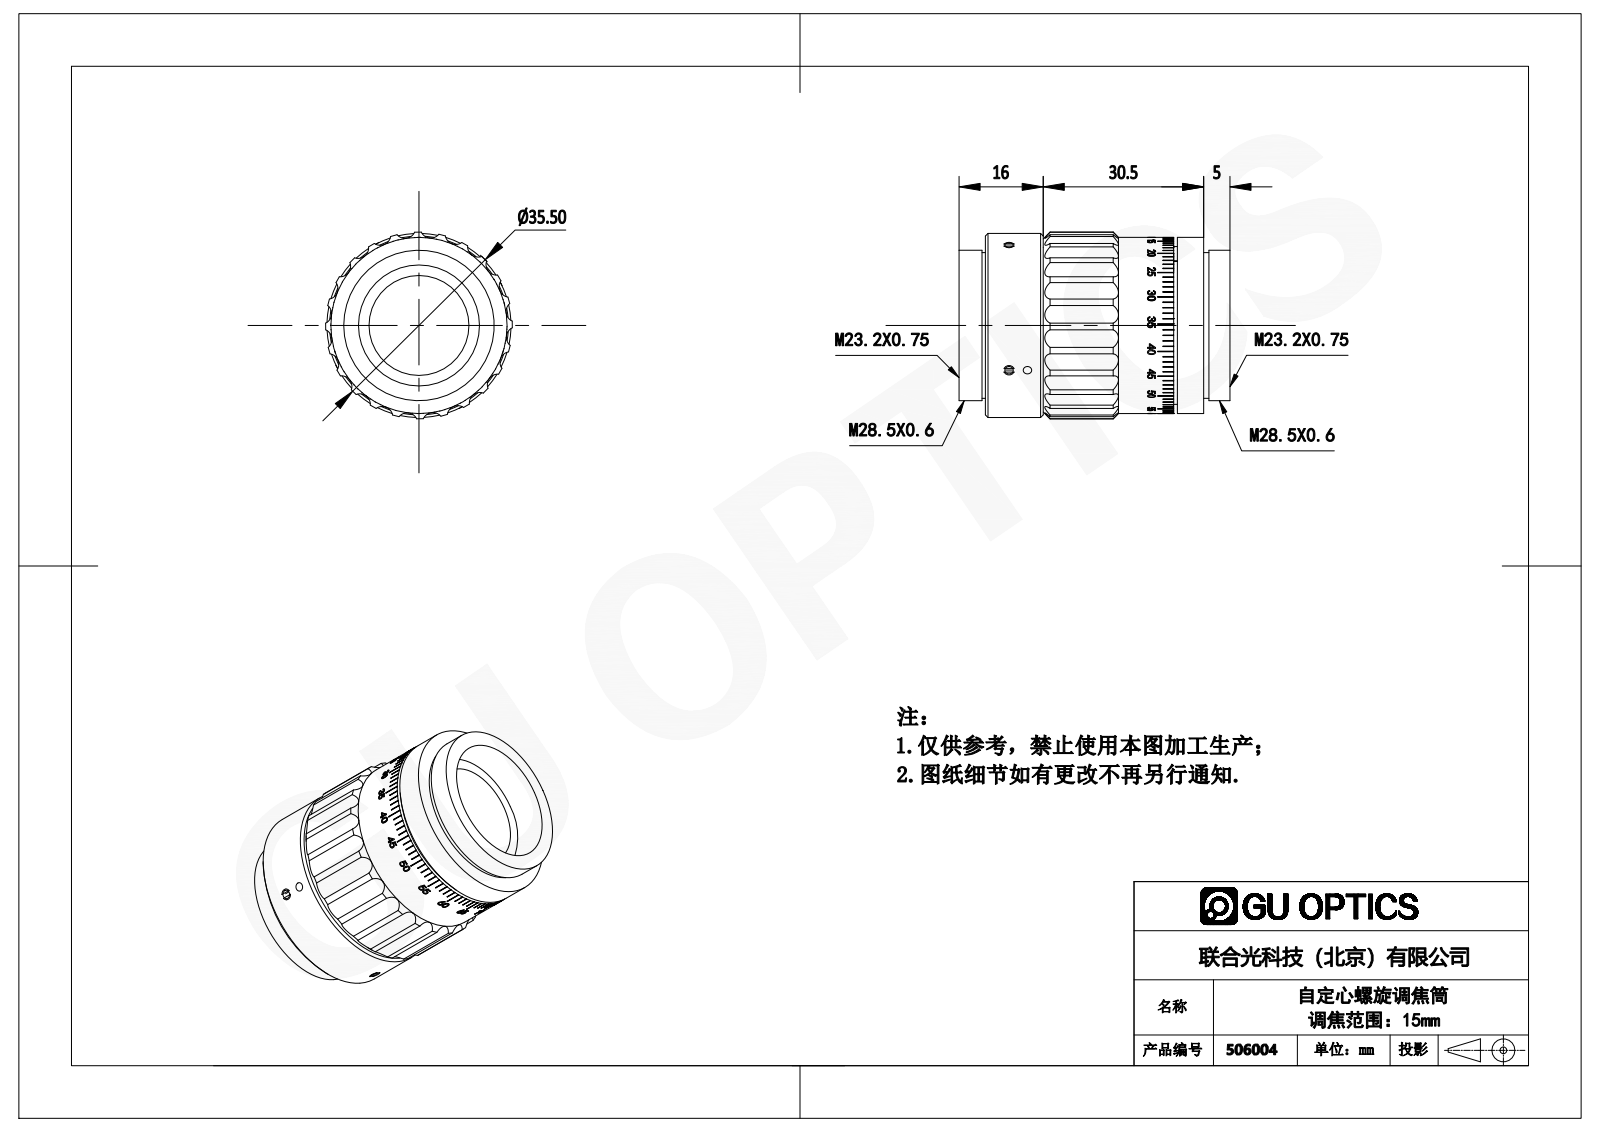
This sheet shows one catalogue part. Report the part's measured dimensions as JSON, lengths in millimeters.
{"part_name": "506004", "step_written_by": "SolidWorks 2016 (AUTOMOTIVE_DESIGN)", "units": "millimeters", "bodies": {"solids": 8, "faces": 1555, "planar": 658, "cylindrical": 347, "other": 550}, "overall_size": [51.5, 35.5, 35.5], "volume_mm3": 26764, "surface_area_mm2": 24360, "round_holes": [[1.6, 5], [2.1, 2], [19, 1], [23, 1], [25, 1], [25.5, 1], [25.7, 1], [28.7, 1], [31, 1], [32, 1]], "round_bosses_or_shafts": [[2.06, 4], [2, 4], [35, 1], [33.5, 1], [31.6, 1], [30.5, 1], [30, 1], [28.6, 1]], "partial_cylinders_radius": [[2, 24], [12.75, 4], [12.5, 2], [14.9, 1], [16.73, 1], [17.75, 1]], "face_to_face_distances": [5, 2, 12, 11.8, 1, 29.7, 34.7, 46.5, 41.5, 10], "hole_center_spacings": [3.5]}
